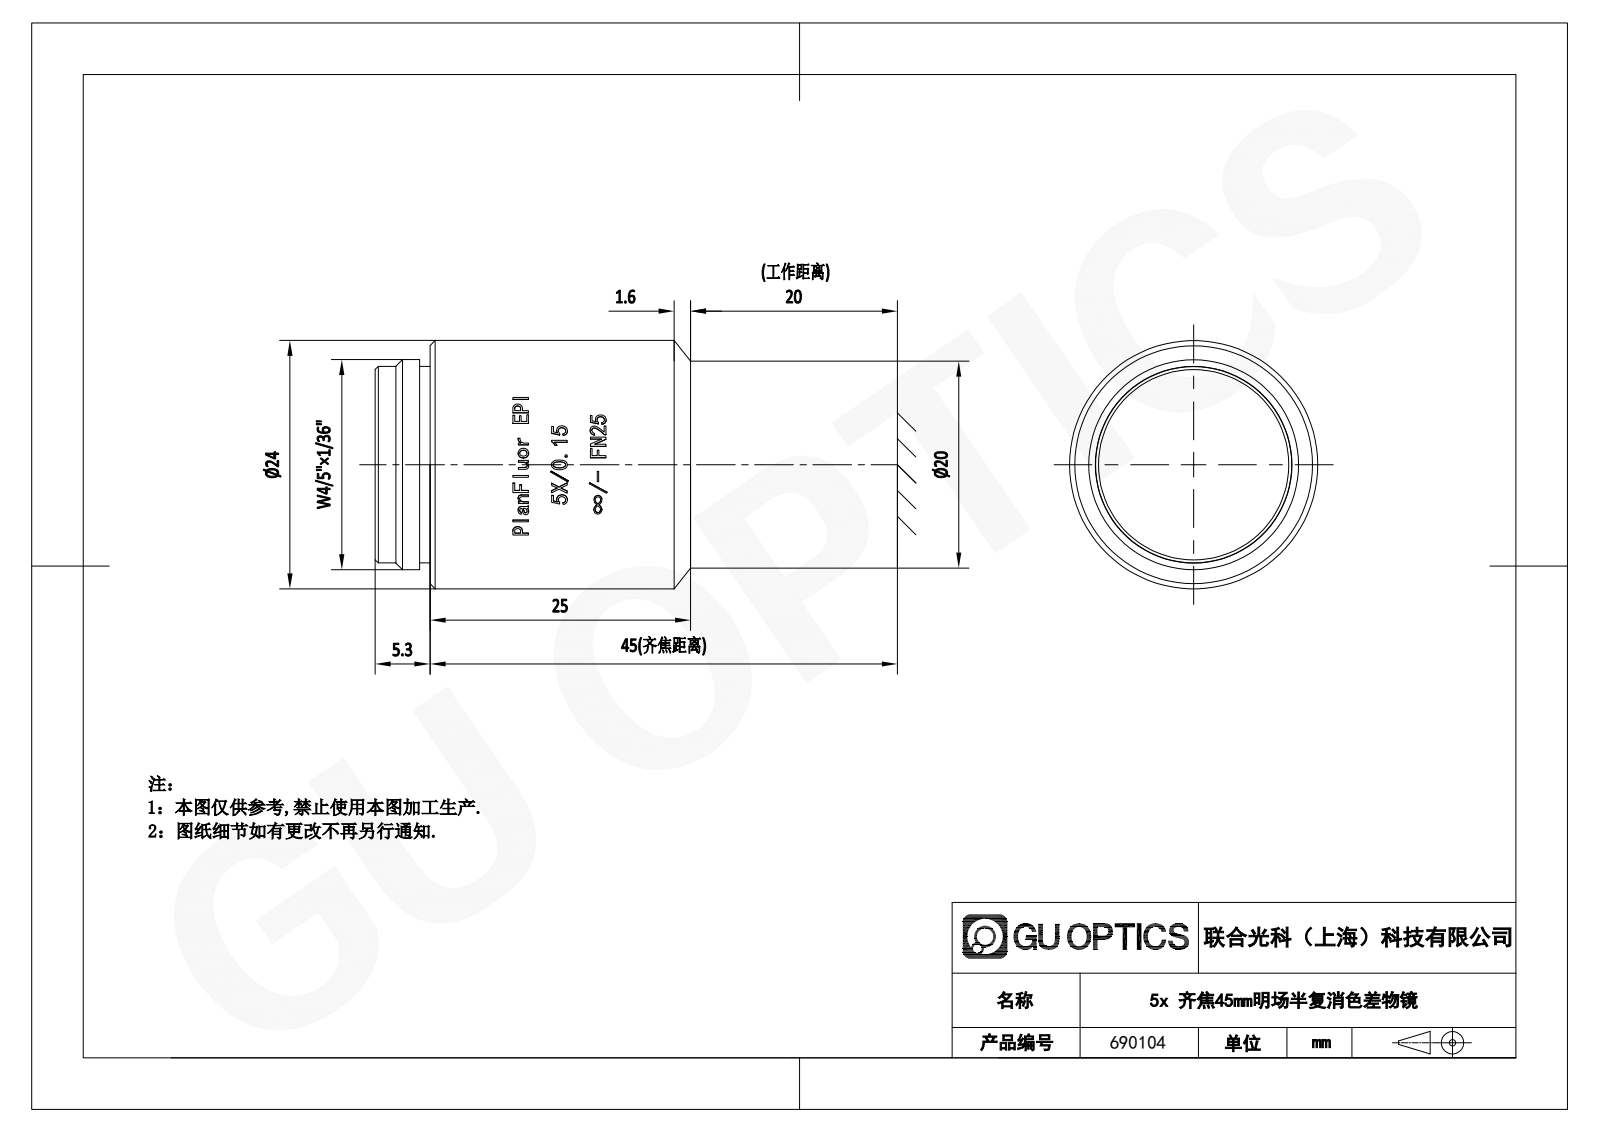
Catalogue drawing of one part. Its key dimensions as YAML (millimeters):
part_name: "690104"
step_written_by: "SolidWorks 2020 (CONFIG_CONTROL_DESIGN)"
units: millimeters
bodies: {solids: 1, faces: 293, planar: 135, cylindrical: 41, other: 117}
overall_size: [30.5, 24.05, 24]
volume: 12858
surface_area: 3080
round_bosses_or_shafts:
  - {diameter: 24, count: 1}
  - {diameter: 20.32, count: 1}
  - {diameter: 19, count: 1}
partial_cylinders:
  - {radius: 12.05, count: 1}
face_to_face_distances: [30.5, 5.3, 25.2, 4.3, 1, 26.2, 2, 2.3, 3.3, 28.5]
